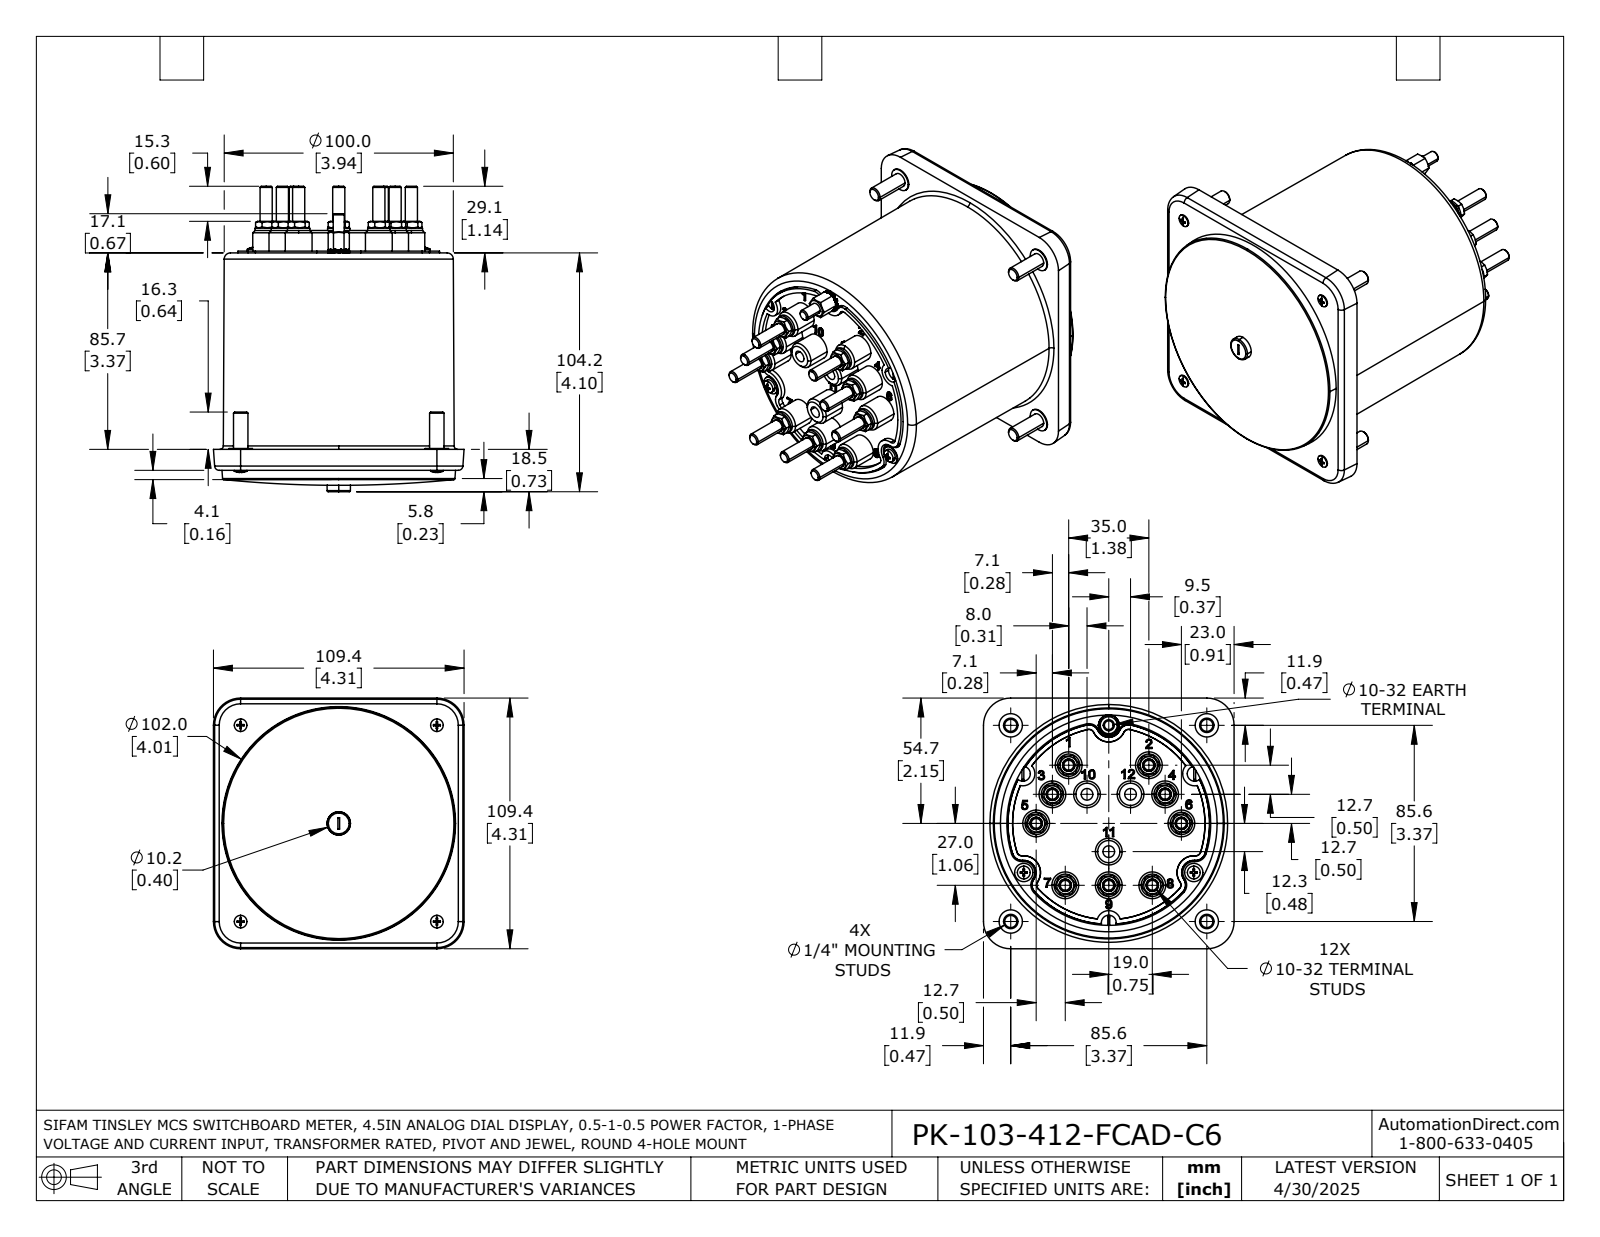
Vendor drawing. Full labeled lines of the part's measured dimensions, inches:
Part name (STEP PRODUCT): PK-103-412-FCAD-C6
STEP written by: SolidWorks 2024 (AUTOMOTIVE_DESIGN)
Units: inches
Bodies: 1 solid, 2018 faces (623 planar, 990 cylindrical, 405 other)
Overall size (bounding box): 5.248 × 4.307 × 4.307
Volume: 51.33 in³ · Surface area: 114.3 in²
Round holes (diameter × count): ⌀0.094 ×4, ⌀0.154 ×3, ⌀0.157 ×3, ⌀0.183 ×3, ⌀0.201 ×3, ⌀0.24 ×3, ⌀0.256 ×3, ⌀0.177 ×2, ⌀0.138 ×1, ⌀0.179 ×1
Round bosses / shafts (diameter × count): ⌀0.461 ×12, ⌀0.384 ×9, ⌀0.209 ×9, ⌀0.402 ×4, ⌀0.248 ×4, ⌀0.217 ×4, ⌀0.232 ×3, ⌀0.175 ×3
Partial cylindrical surfaces — rounded edges, fillets, slot ends (radius × count): R0.009 ×286, R0.043 ×283, R0.027 ×12, R0.177 ×11, R0.027 ×10, R0.189 ×9, R0.079 ×4, R0.207 ×3
Main face-to-face distances: 3.327, 3.687, 0.36, 0.048, 3.375, 3.735, 0.031, 0.079, 3.406, 3.766
Hole centre spacings: 1.696, 1.685, 1.696, 2.922, 3.37, 2.548, 2.922, 2.953
